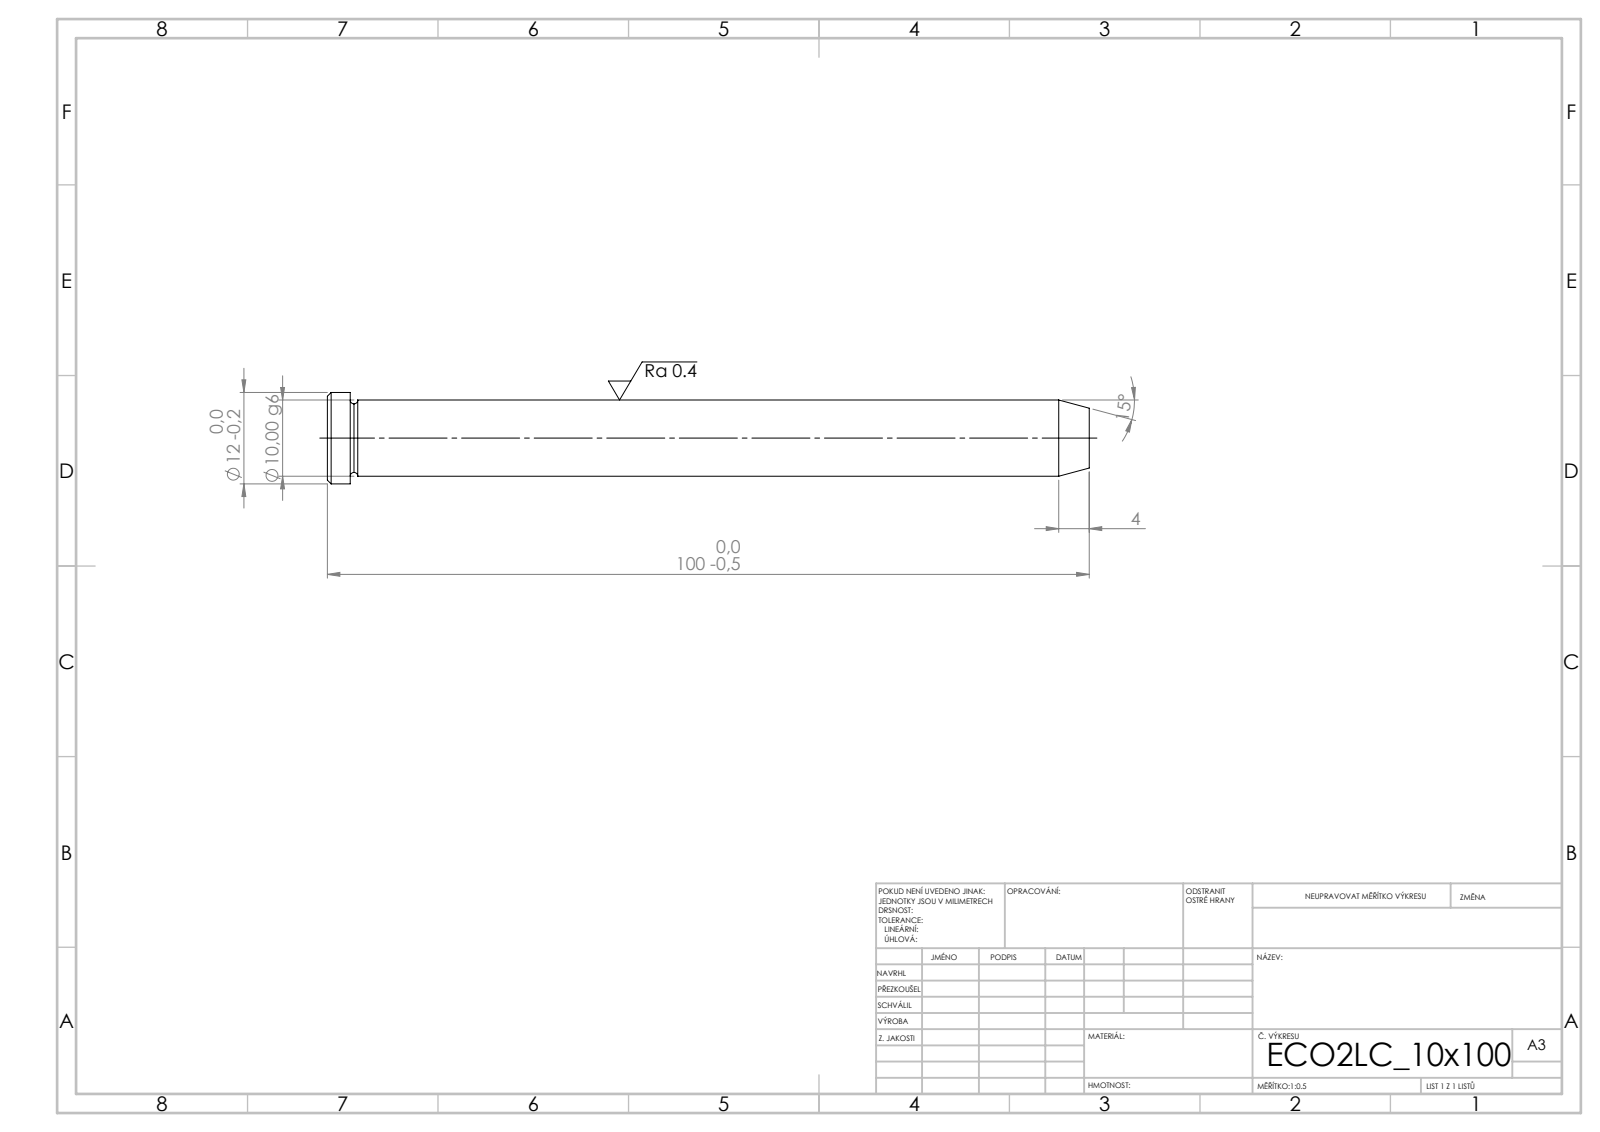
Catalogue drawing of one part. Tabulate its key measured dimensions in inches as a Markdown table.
| quantity | value |
| --- | --- |
| STEP written by | SolidWorks 2019 (CONFIG_CONTROL_DESIGN) |
| units | inches |
| bodies | 1 solid, 15 faces (3 planar, 4 cylindrical, 8 other) |
| overall size | 3.937 × 0.472 × 0.472 |
| volume | 0.481 in³ |
| surface area | 5.193 in² |
| round bosses / shafts (diameter × count) | 0.472 × 1, 0.394 × 1 |
| main face-to-face distances | 3.937, 3.819, 0.118 |
